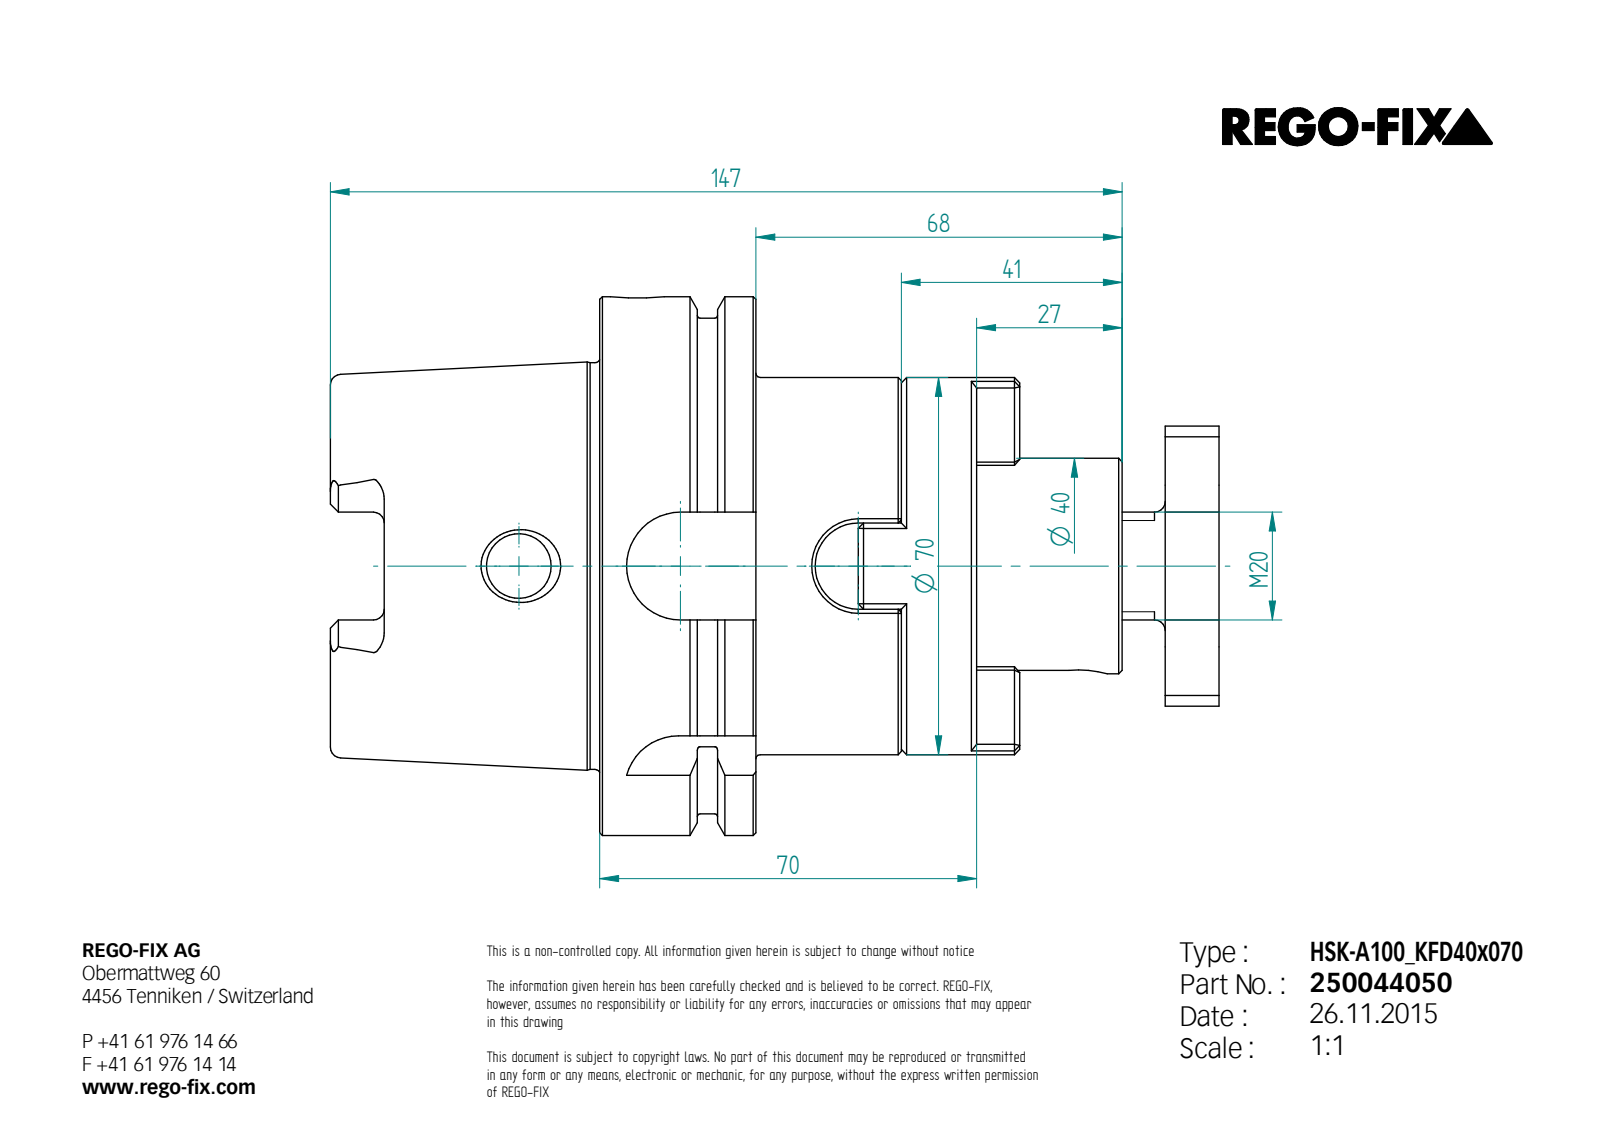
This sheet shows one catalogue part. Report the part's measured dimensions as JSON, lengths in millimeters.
{"step_written_by": "Unknown (AUTOMOTIVE_DESIGN)", "units": "millimeters", "bodies": {"solids": 3, "faces": 255, "planar": 125, "cylindrical": 52, "other": 78}, "overall_size": [165, 100, 100], "volume_mm3": 455386, "surface_area_mm2": 83123, "round_holes": [[12, 2], [8.5, 1], [10, 1], [17.29, 1], [21, 1], [22.38, 1], [25, 1], [40, 1], [53, 1], [63, 1]], "round_bosses_or_shafts": [[100, 1], [92, 1], [75.46, 1], [70, 1], [39.4, 1], [20, 1]], "partial_cylinders_radius": [[2, 6], [5, 6], [4.88, 4], [10, 2], [8, 1], [11, 1], [26, 1]], "face_to_face_distances": [27, 29, 56, 41, 49, 12.5, 115, 70, 14, 86]}
